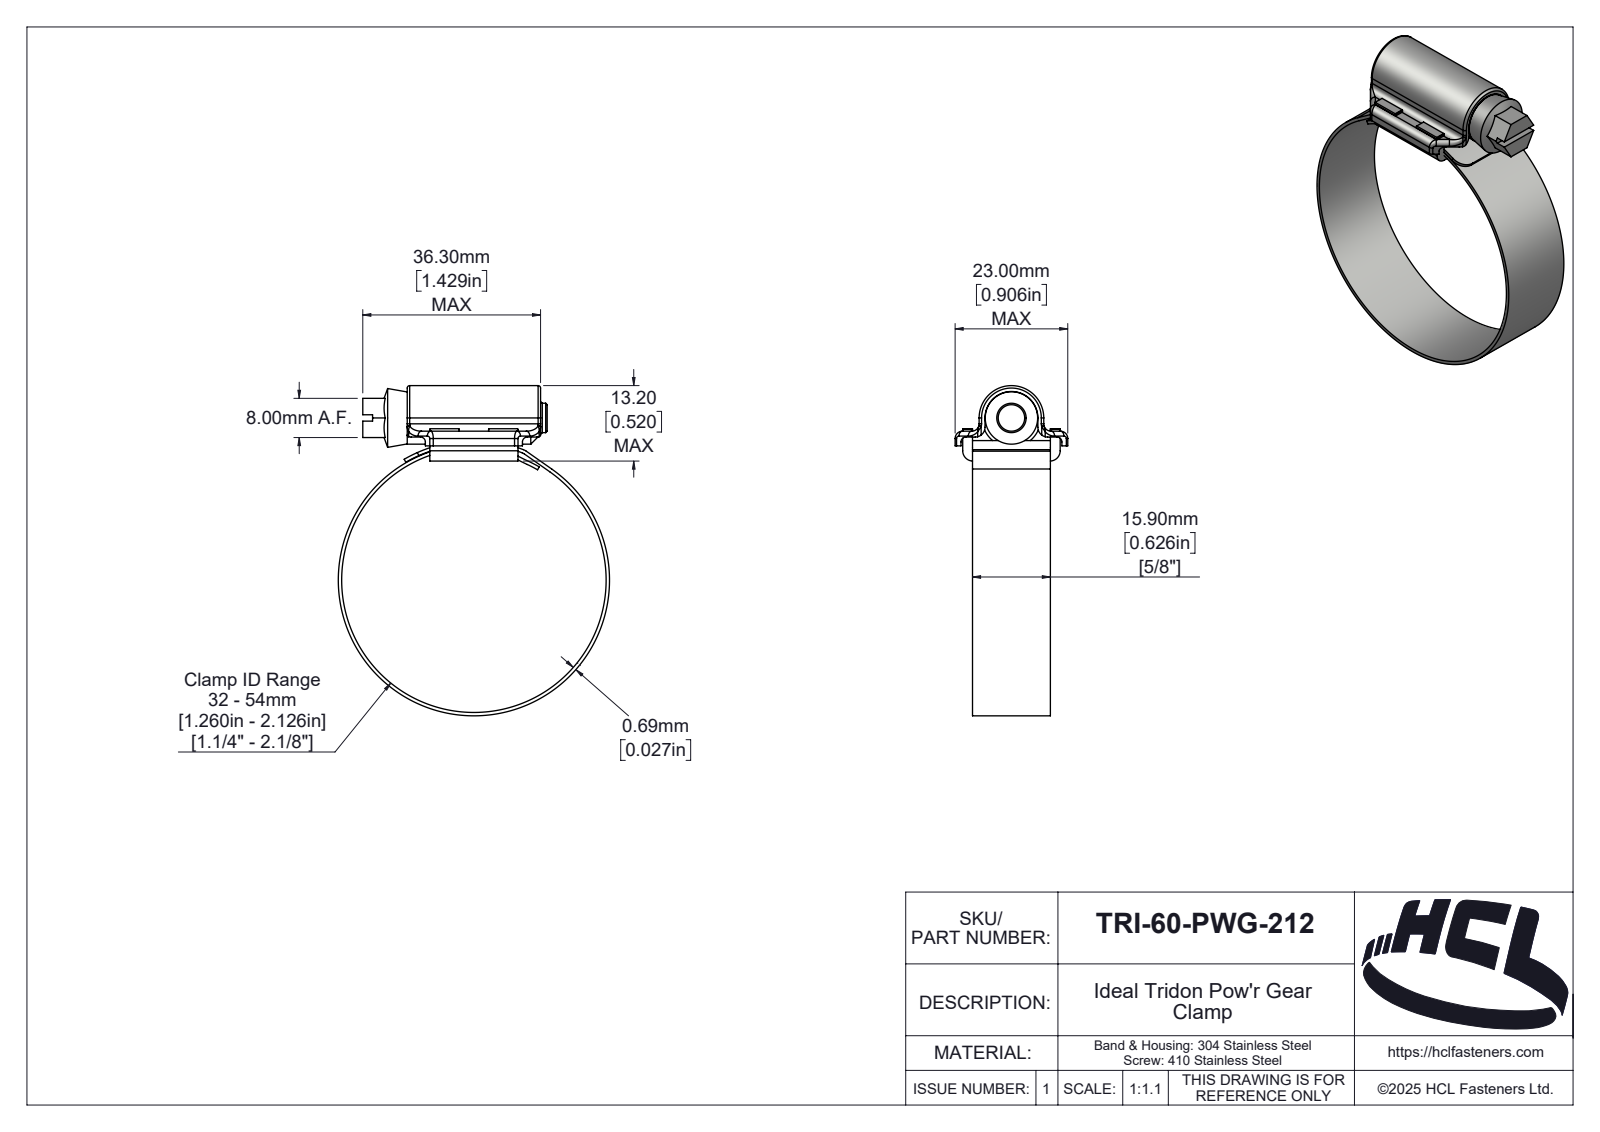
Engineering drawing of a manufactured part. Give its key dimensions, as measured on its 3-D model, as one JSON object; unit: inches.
{"part_name": "TRI-60-PWG-212", "step_written_by": "SolidWorks 2025 (AUTOMOTIVE_DESIGN)", "units": "inches", "bodies": {"solids": 4, "faces": 268, "planar": 87, "cylindrical": 102, "other": 79}, "overall_size": [2.653, 2.18, 0.906], "volume_in3": 0.451, "surface_area_in2": 17.47, "round_holes": [[2.126, 1]], "round_bosses_or_shafts": [[2.18, 1], [0.421, 1], [0.236, 1]], "partial_cylinders_radius": [[0.039, 14], [0.02, 4], [0.059, 4], [0.079, 3], [0.004, 2], [0.083, 2], [0.118, 2], [0.018, 1]], "face_to_face_distances": [0.079, 0.626, 0.705, 0.193, 0.047, 0.179, 0.132, 0.604, 0.1, 0.526]}
